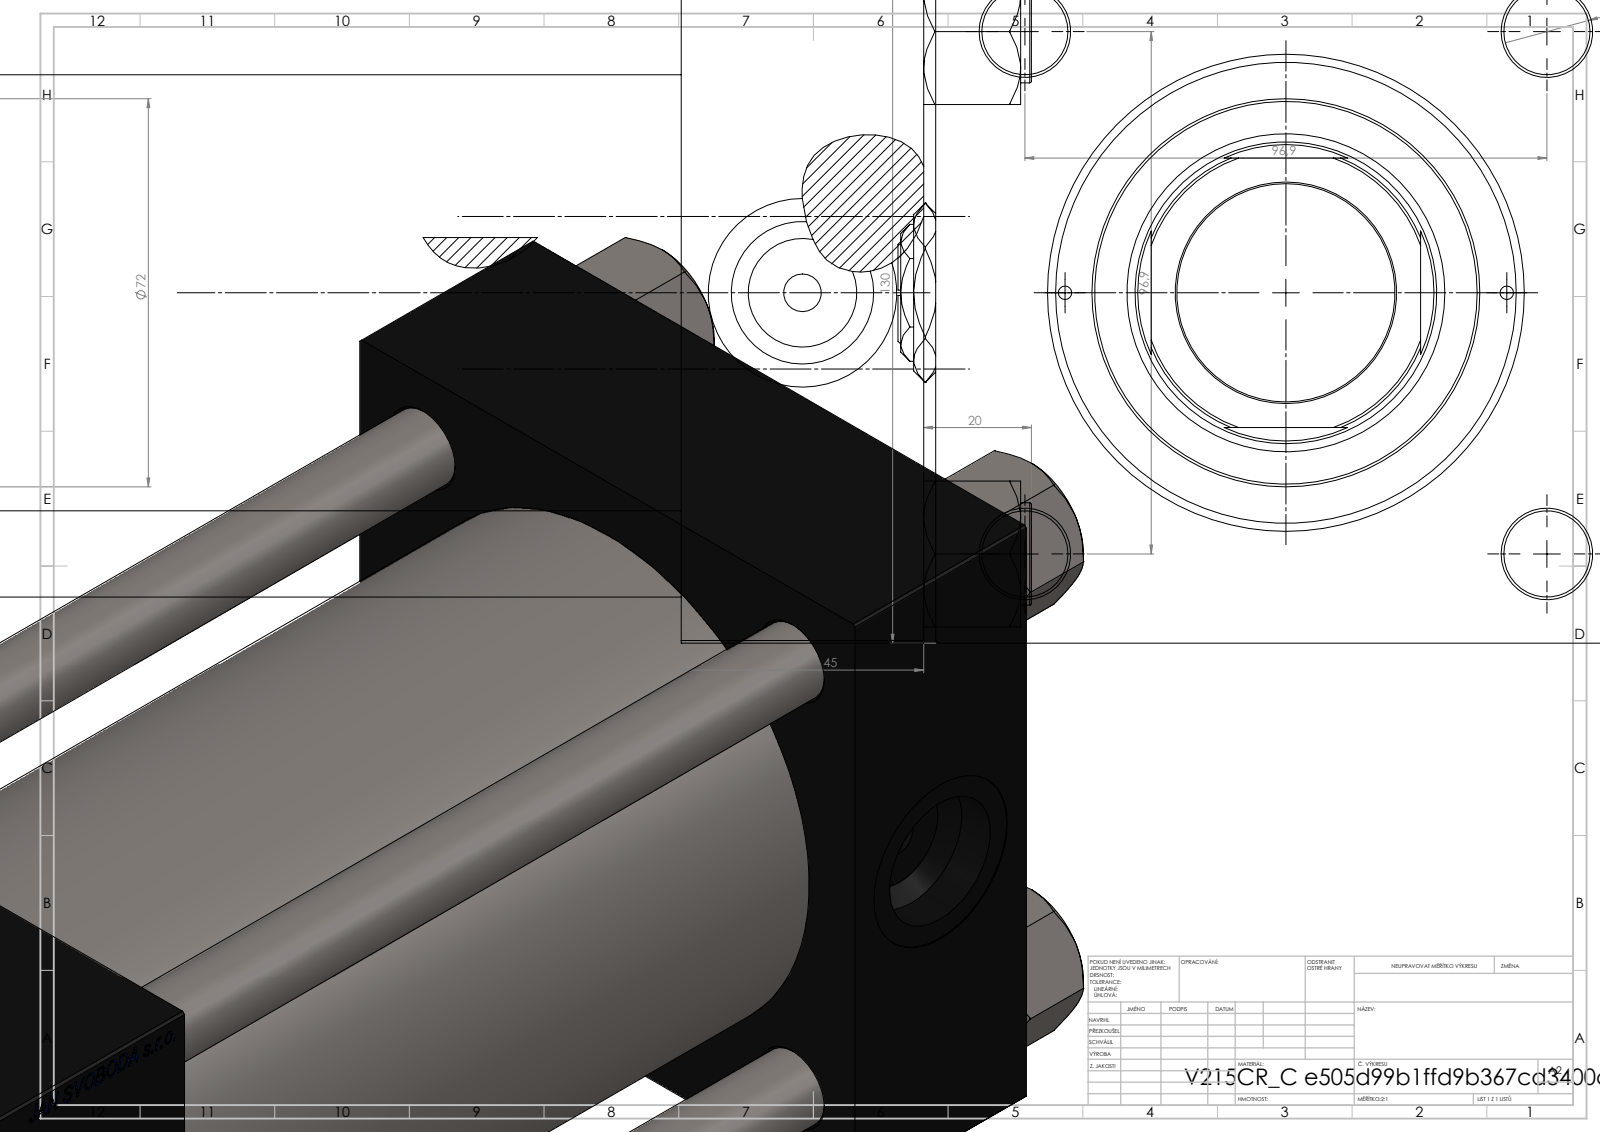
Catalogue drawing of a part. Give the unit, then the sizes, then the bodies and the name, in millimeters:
Units: millimetres
Overall size (bounding box): 348 × 144 × 130
Round holes (diameter × count): ⌀16 ×4, ⌀2.5 ×2, ⌀7 ×2, ⌀26.44 ×2, ⌀35 ×2, ⌀40.5 ×1, ⌀56 ×1, ⌀59 ×1, ⌀76 ×1, ⌀85.5 ×1, ⌀100 ×1
Round bosses / shafts (diameter × count): ⌀19 ×4, ⌀106 ×1, ⌀72 ×1
Partial cylindrical surfaces — rounded edges, fillets, slot ends (radius × count): R27 ×1
Main face-to-face distances: 130, 45, 293, 248, 221, 176, 72, 51, 125, 197
Hole centre spacings: 49.02, 68.52, 96.9, 101.73, 41, 137.04, 82, 223.5
Volume: 2 906 000 mm³ · Surface area: 448 047 mm²
Bodies: 13 solids, 1303 faces (623 planar, 102 cylindrical, 578 other)
Part name (STEP PRODUCT): NUT_M5_C; V215CR_C_Body; Zatka_pro_OIL_PORT; V215CR_VCP_C (+2 more)
STEP written by: SolidWorks 2019 (CONFIG_CONTROL_DESIGN)
